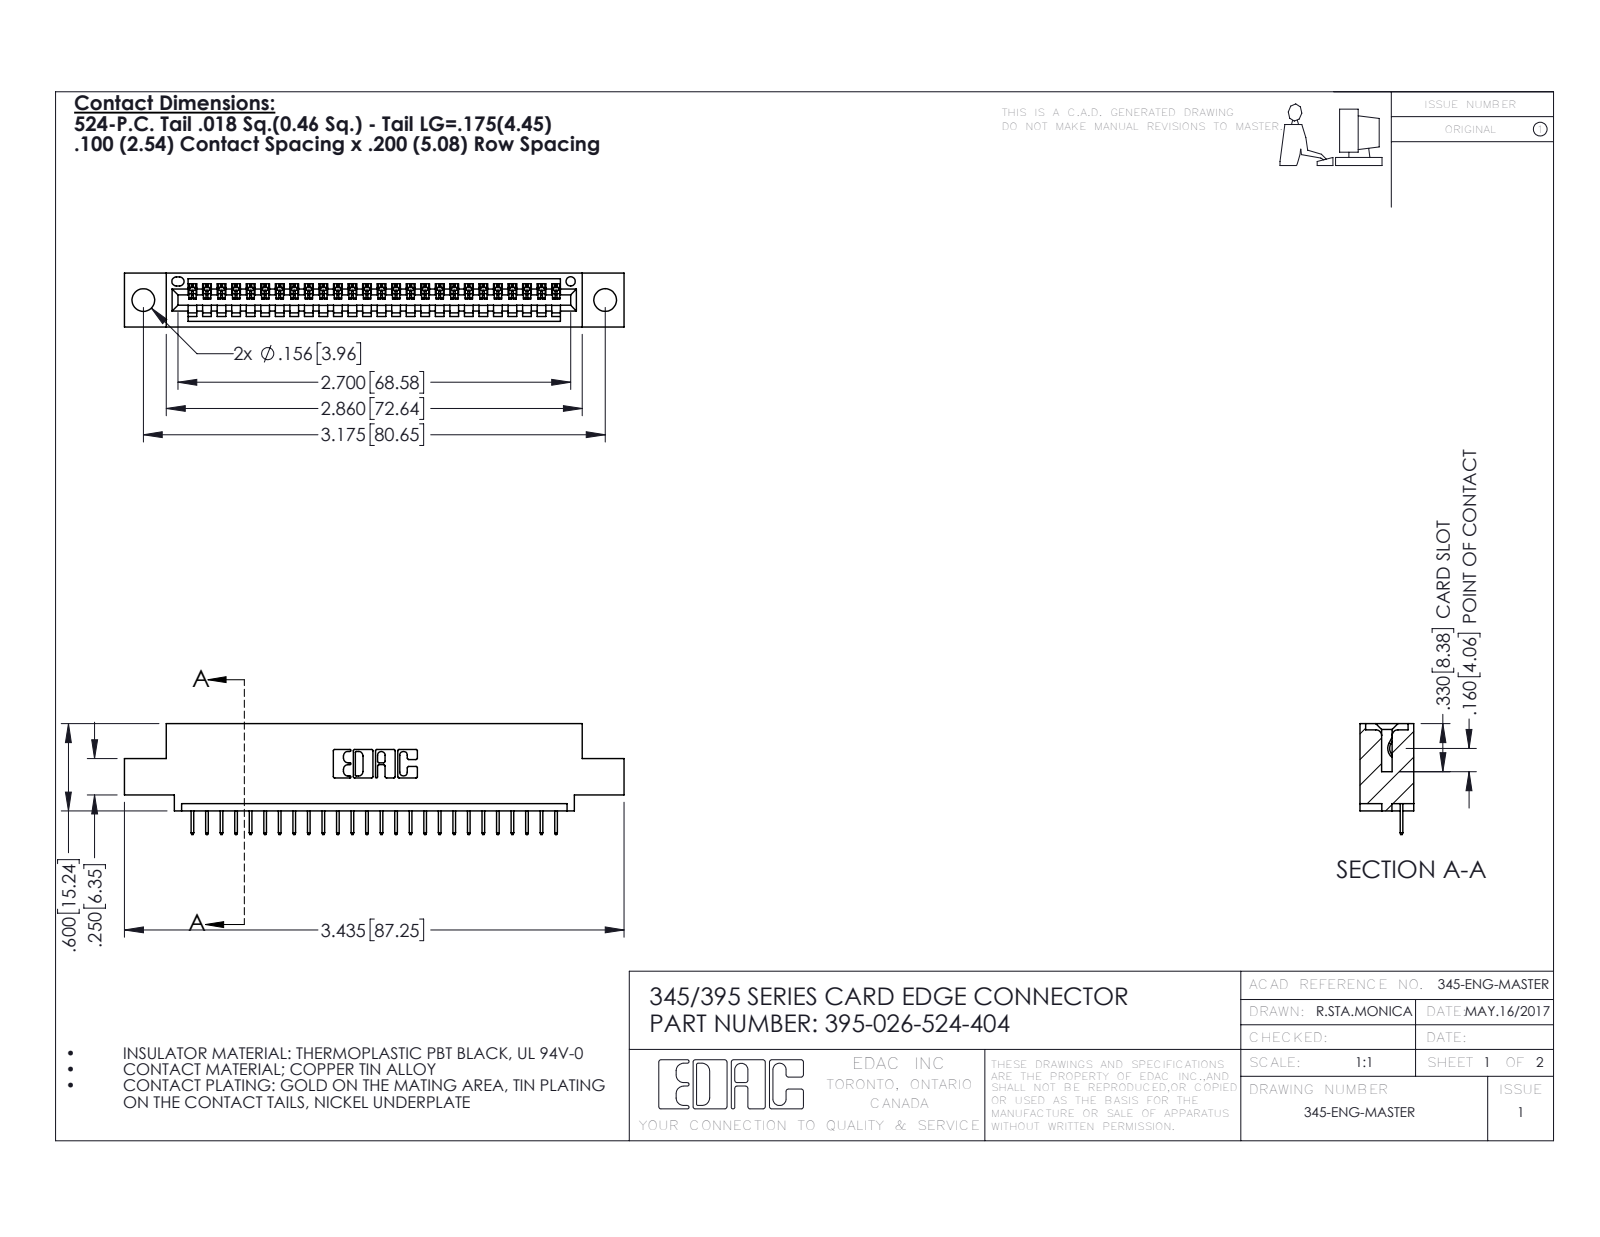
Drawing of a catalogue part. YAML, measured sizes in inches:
part_name: "345-292-001_345-293-124; 345 Part_0.110 Offset - 0.156 Dia-TH; 395-026-524-404"
step_written_by: "SolidWorks 2016 (CONFIG_CONTROL_DESIGN)"
units: inches
bodies: {solids: 27, faces: 1742, planar: 1280, cylindrical: 462, other: 0}
overall_size: [3.435, 0.762, 0.37]
volume: 0.482
surface_area: 15.24
round_holes:
  - {diameter: 0.156, count: 2}
  - {diameter: 0.064, count: 1}
partial_cylinders:
  - {radius: 0.006, count: 52}
  - {radius: 0.01, count: 22}
  - {radius: 0.007, count: 6}
  - {radius: 0.031, count: 6}
  - {radius: 0.026, count: 3}
  - {radius: 0.031, count: 2}
  - {radius: 0.04, count: 2}
  - {radius: 0.014, count: 1}
face_to_face_distances: [0.072, 0.298, 0.37, 0.2, 0.098, 0.272, 0.025, 0.225, 0.072, 0.149]
hole_center_spacings: [0.27, 2.94, 3.175]
